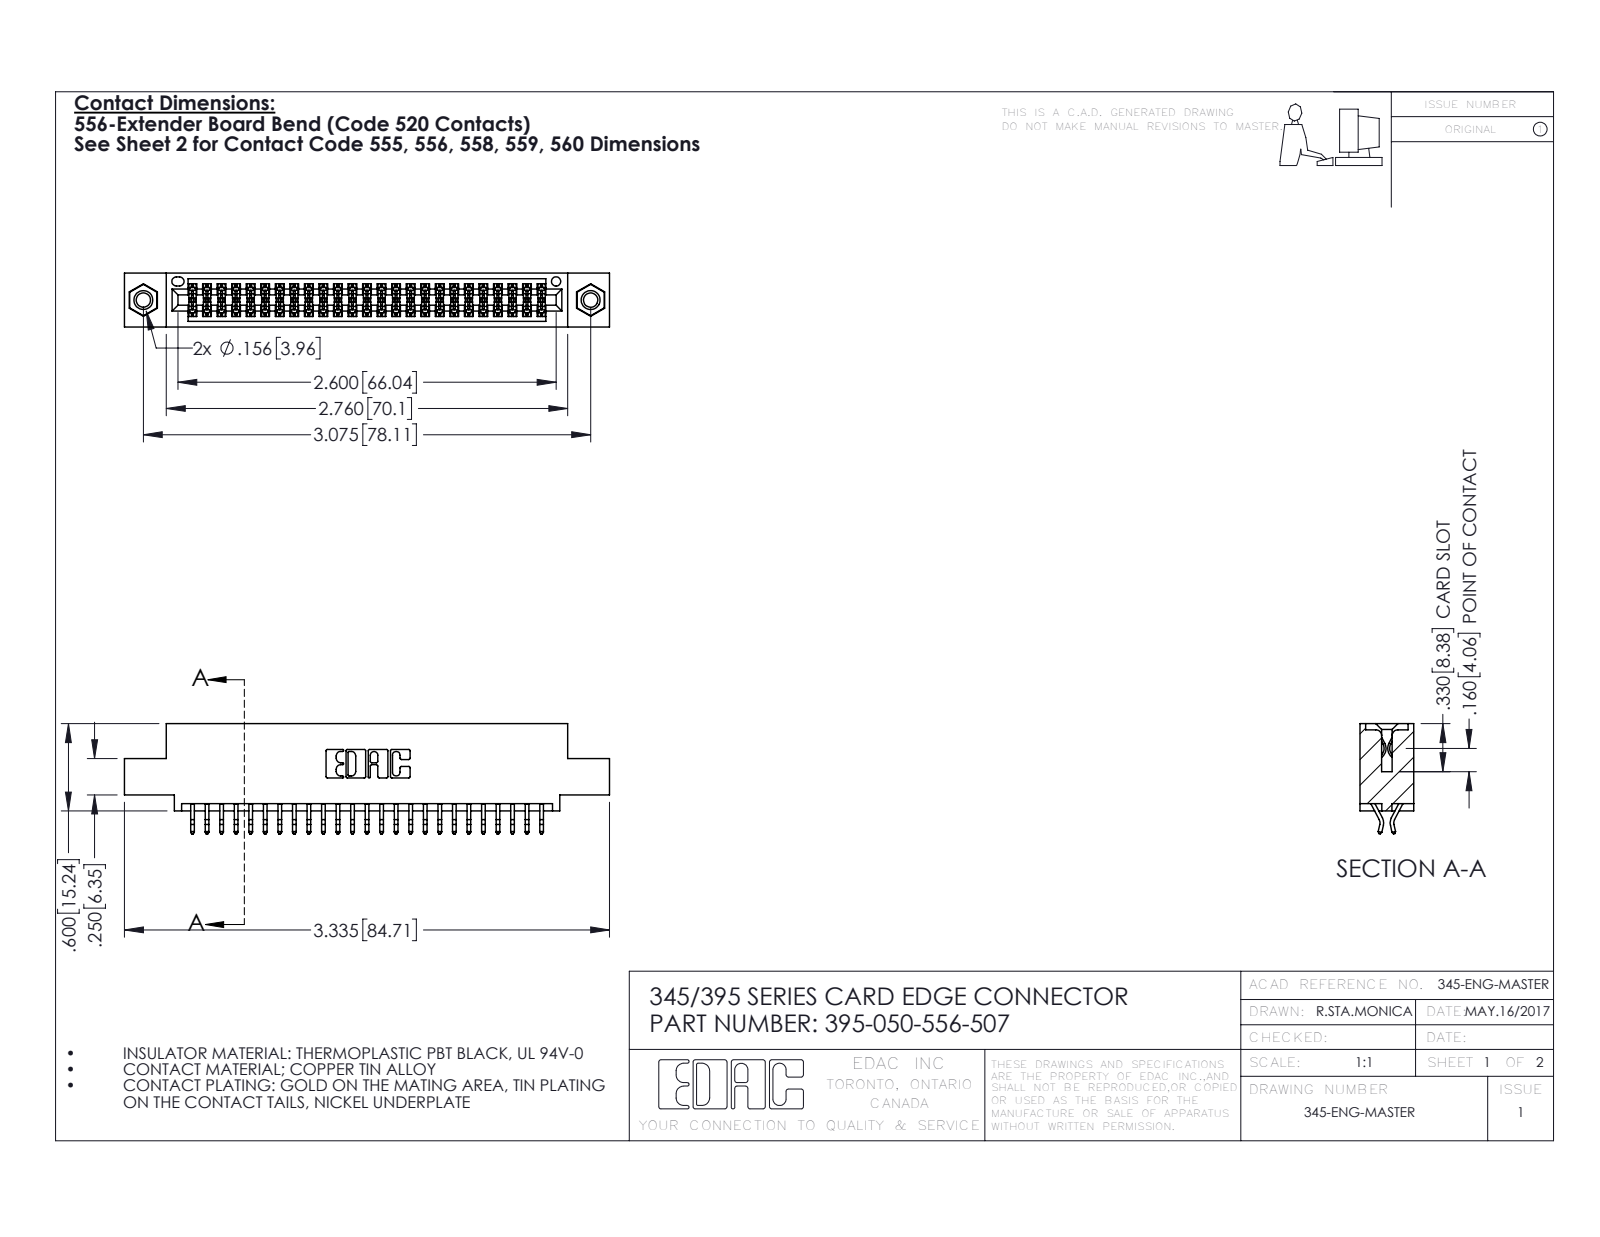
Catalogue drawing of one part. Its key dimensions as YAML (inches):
part_name: "395-050-556-507; 345-250-001_345-250-005-103; 345-292-001_556 Tail; 345 Part_0.110 Offset - 0.156 Dia-TI"
step_written_by: "SolidWorks 2016 (CONFIG_CONTROL_DESIGN)"
units: inches
bodies: {solids: 53, faces: 2990, planar: 1966, cylindrical: 1008, other: 16}
overall_size: [3.335, 0.757, 0.37]
volume: 0.487
surface_area: 17.9
round_holes:
  - {diameter: 0.098, count: 2}
  - {diameter: 0.125, count: 2}
  - {diameter: 0.156, count: 2}
  - {diameter: 0.064, count: 1}
round_bosses_or_shafts:
  - {diameter: 0.155, count: 2}
partial_cylinders:
  - {radius: 0.006, count: 75}
  - {radius: 0.01, count: 22}
  - {radius: 0.007, count: 6}
  - {radius: 0.031, count: 6}
  - {radius: 0.026, count: 3}
  - {radius: 0.01, count: 2}
  - {radius: 0.014, count: 2}
  - {radius: 0.019, count: 2}
face_to_face_distances: [0.072, 0.298, 0.2, 0.37, 0.025, 0.098, 0.272, 0.225, 0.175, 0.149]
hole_center_spacings: [0.27, 2.84, 3.075]
